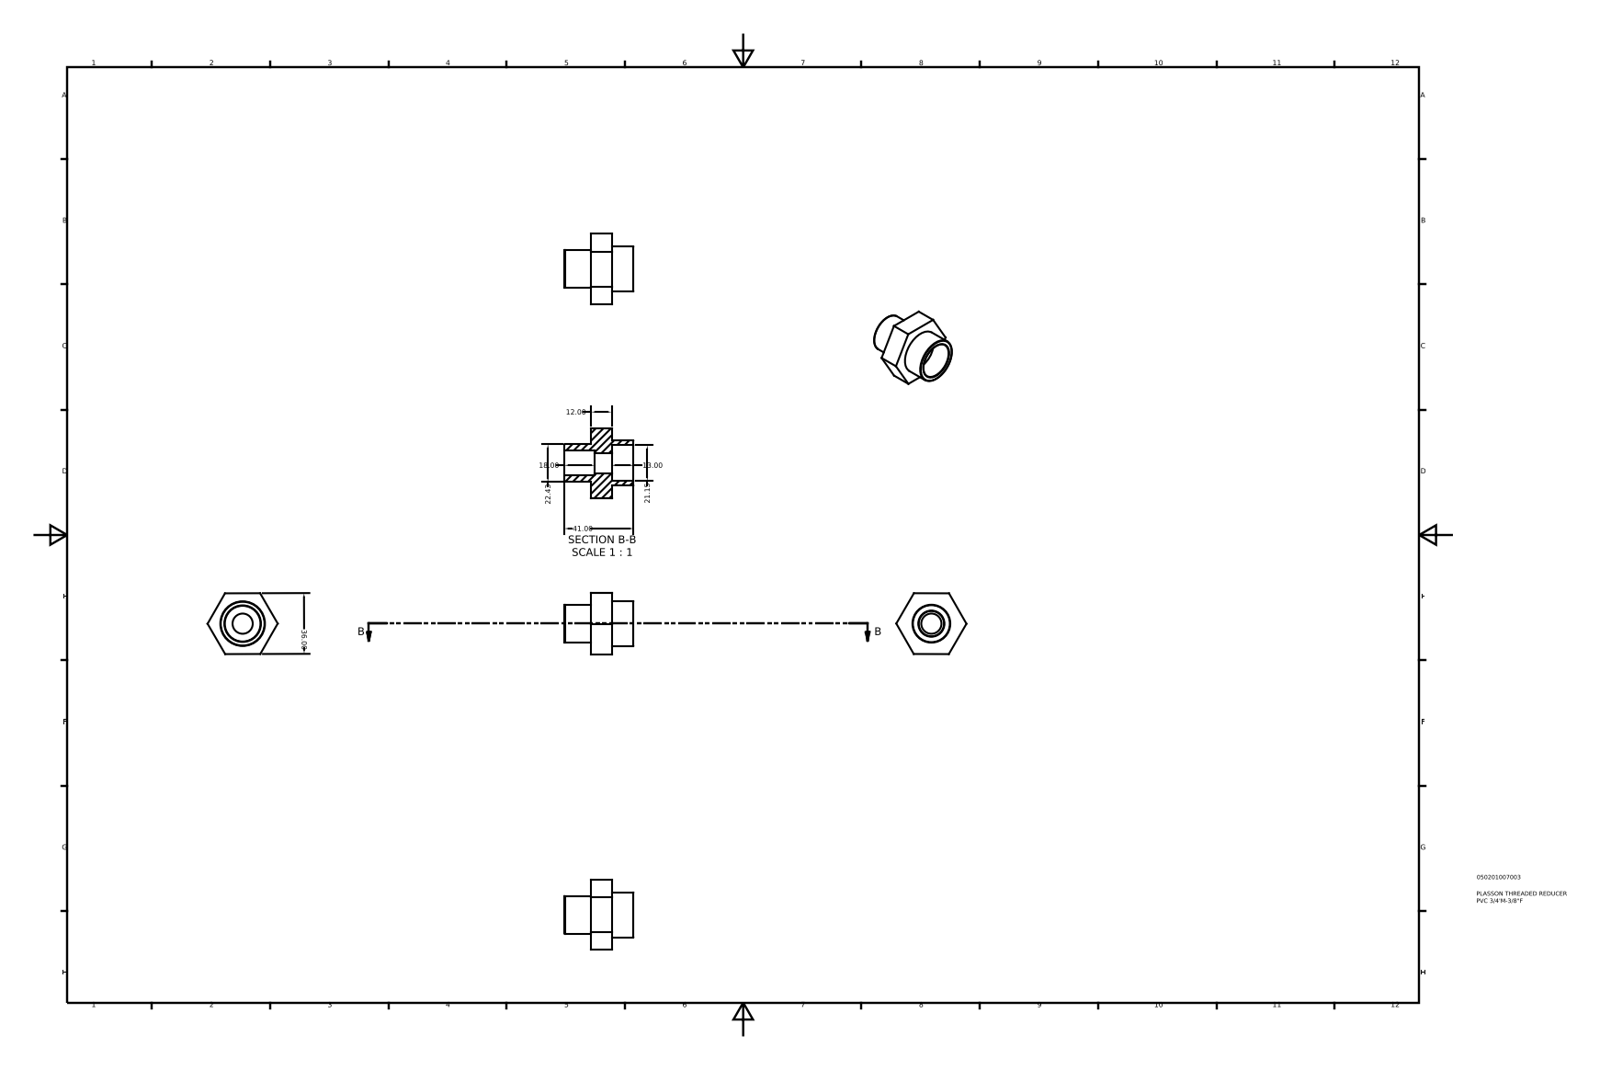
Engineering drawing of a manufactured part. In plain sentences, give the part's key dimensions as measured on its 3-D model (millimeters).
The part is named "050201007003". Its 3-D file was written by "Autodesk Inventor 2015 (AUTOMOTIVE_DESIGN)". It is 1 solid with 21 faces: 12 planar, 5 cylindrical and 4 other. Overall it measures 41.57 by 41 by 36.06 millimeters. Its volume is 18 070 cubic millimeters and its surface area 7 778 square millimeters. Round holes: 1 of diameter 11.96, 1 of diameter 14.95, 1 of diameter 21.15. Round bosses or shafts: 1 of diameter 26.44, 1 of diameter 22.43. The main face-to-face distances are 12, 36.02, 36, 16, 28, 41, 25, 13, 18, 2.
